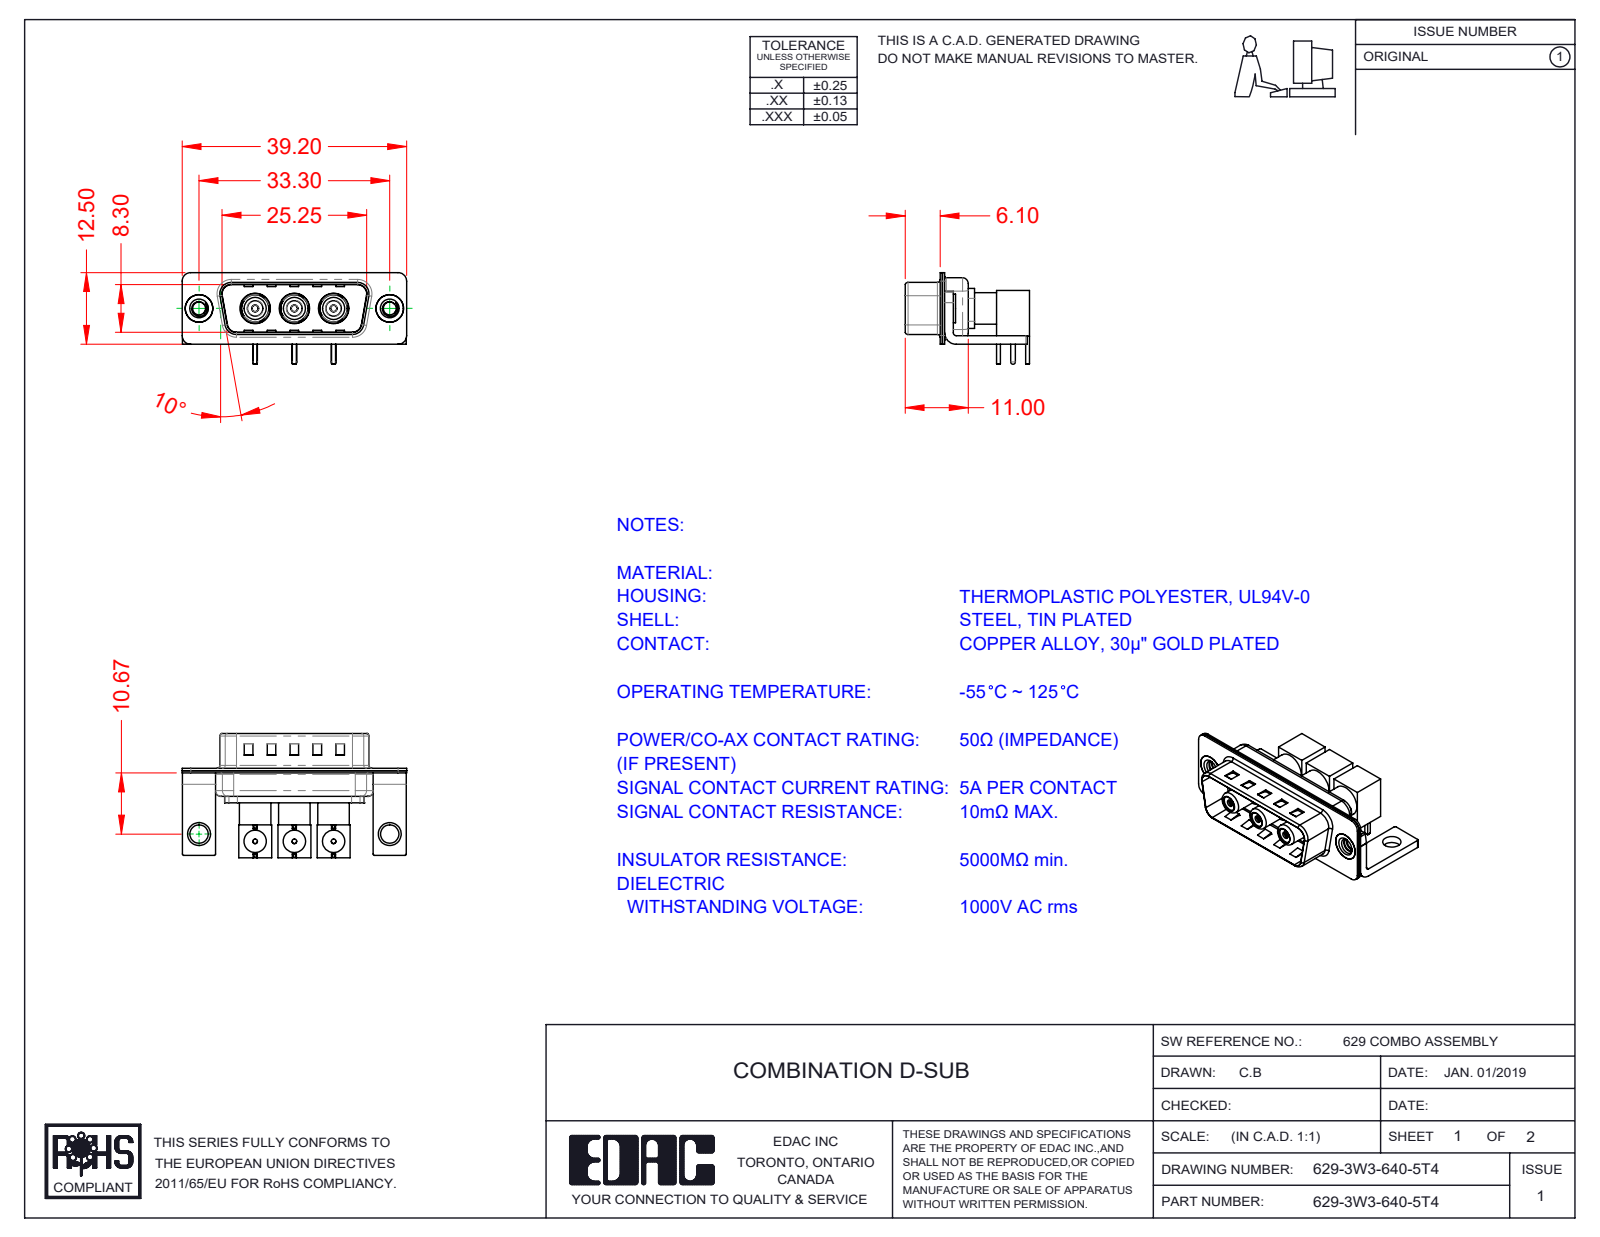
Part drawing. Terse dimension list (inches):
name: Insulator RA Pin; 629Combo Threaded Rivet_3; RA Back Shell; Co-Ax Jack Assy_RA (+8 more)
written by: SolidWorks 2020 (CONFIG_CONTROL_DESIGN)
unit: in
bodies: 28 solids, 836 faces (330 planar, 352 cylindrical, 154 other)
size: 1.543 × 0.855 × 0.63
volume: 0.181 in³; area: 12.57 in²
holes: 3× ⌀0.031, 3× ⌀0.043, 3× ⌀0.047, 3× ⌀0.059, 3× ⌀0.063, 3× ⌀0.098, 3× ⌀0.106, 3× ⌀0.122, 3× ⌀0.134, 3× ⌀0.154, 3× ⌀0.161, 3× ⌀0.191
bosses: 6× ⌀0.031, 3× ⌀0.217, 3× ⌀0.205, 3× ⌀0.189, 3× ⌀0.186, 3× ⌀0.164, 3× ⌀0.157, 3× ⌀0.152
rounds: 16× R0.01, 16× R0.059, 13× R0.079, 9× R0.02, 8× R0.063, 4× R0.024, 4× R0.026, 4× R0.035
face distances: 0.016, 0.031, 0.059, 0.226, 0.374, 0.055, 0.358, 0.043, 0.014, 0.27
hole spacings: 0.27, 0.539, 0.389, 0.657, 0.926, 0.386, 0.656, 0.925
